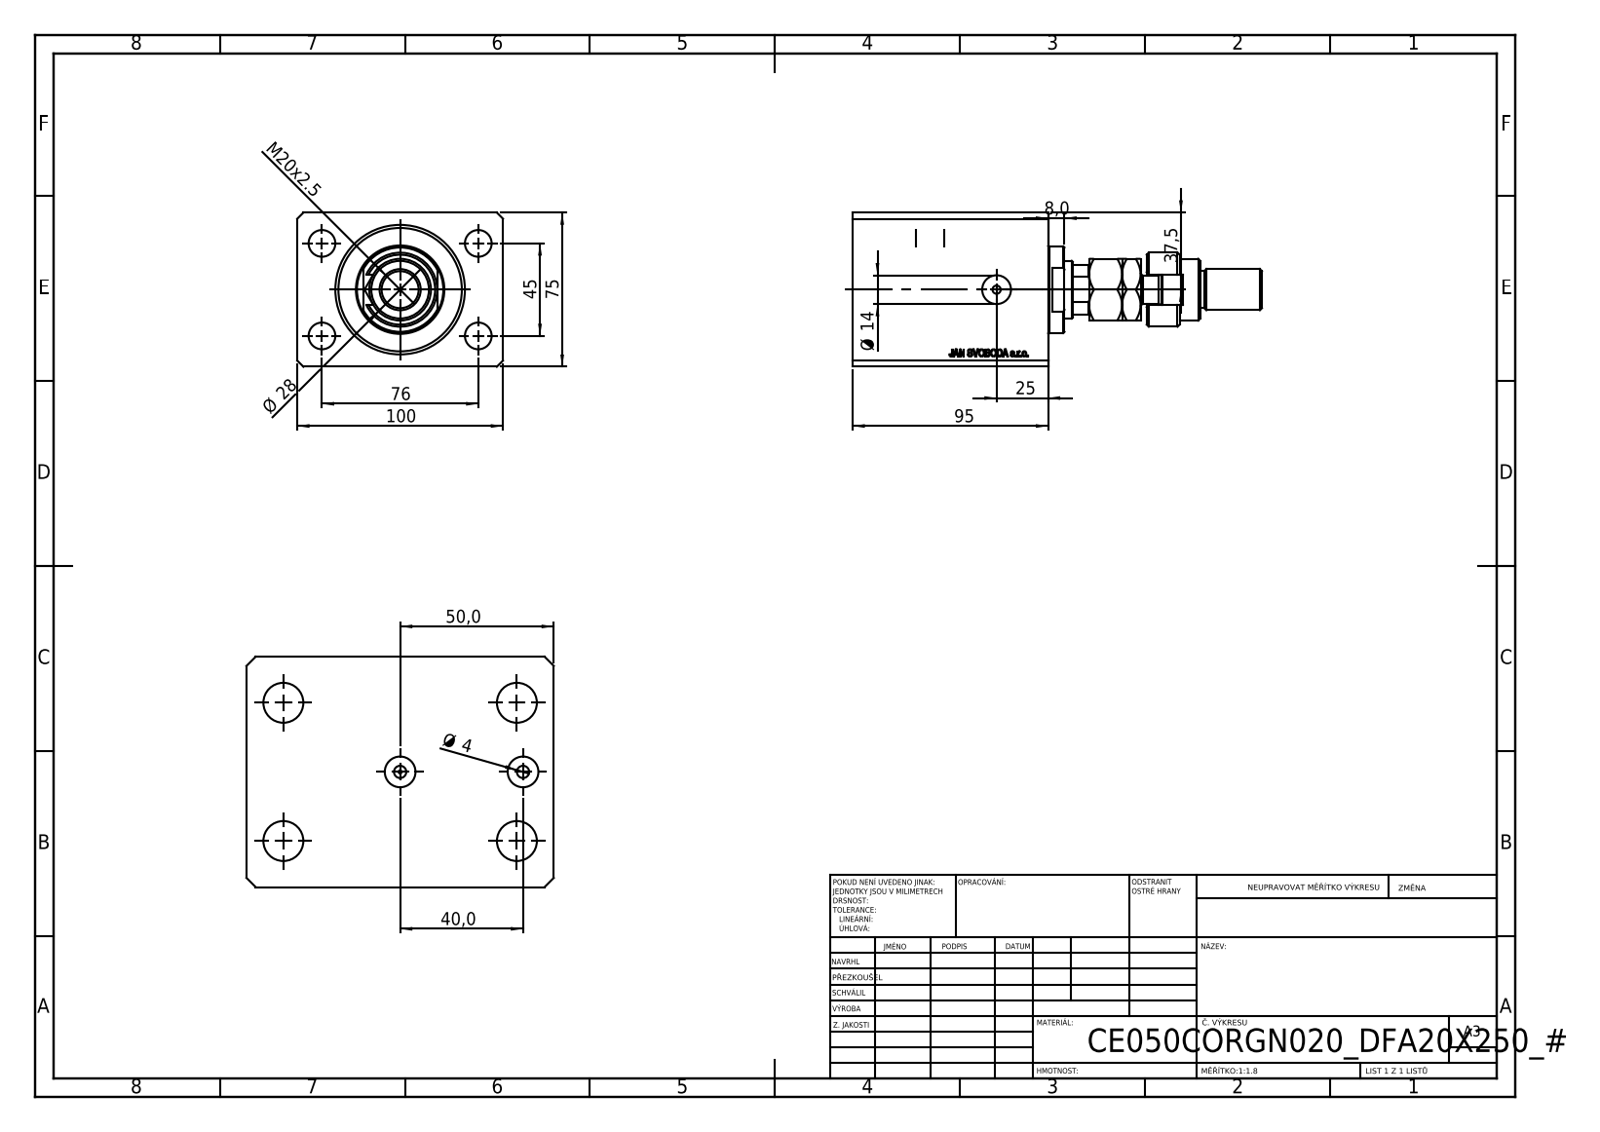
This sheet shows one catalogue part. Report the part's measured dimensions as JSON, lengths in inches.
{"part_name": "V250CE_C_Body; FEMALE_PART_FOR_DFA; MFA; V250CE_VC_C (+1 more)", "step_written_by": "SolidWorks 2019 (CONFIG_CONTROL_DESIGN)", "units": "inches", "bodies": {"solids": 5, "faces": 953, "planar": 456, "cylindrical": 59, "other": 438}, "overall_size": [7.835, 3.937, 2.953], "volume_in3": 41.88, "surface_area_in2": 189.1, "round_holes": [[0.157, 4], [0.512, 4], [0.394, 2], [0.551, 2], [0.049, 1], [0.728, 1], [1.102, 1], [1.969, 1], [2.48, 1]], "round_bosses_or_shafts": [[1.654, 1], [1.417, 1], [1.181, 1], [0.866, 1], [0.787, 1], [0.709, 1], [0.551, 1]], "partial_cylinders_radius": [[0.295, 1], [0.472, 1], [0.531, 1]], "face_to_face_distances": [2.953, 3.937, 0.787, 3.74, 0.469, 3.272, 2.484, 1.575, 1.181, 2.165], "hole_center_spacings": [1.739, 1.772, 0.889, 2.992, 3.196, 3.477, 1.575]}
